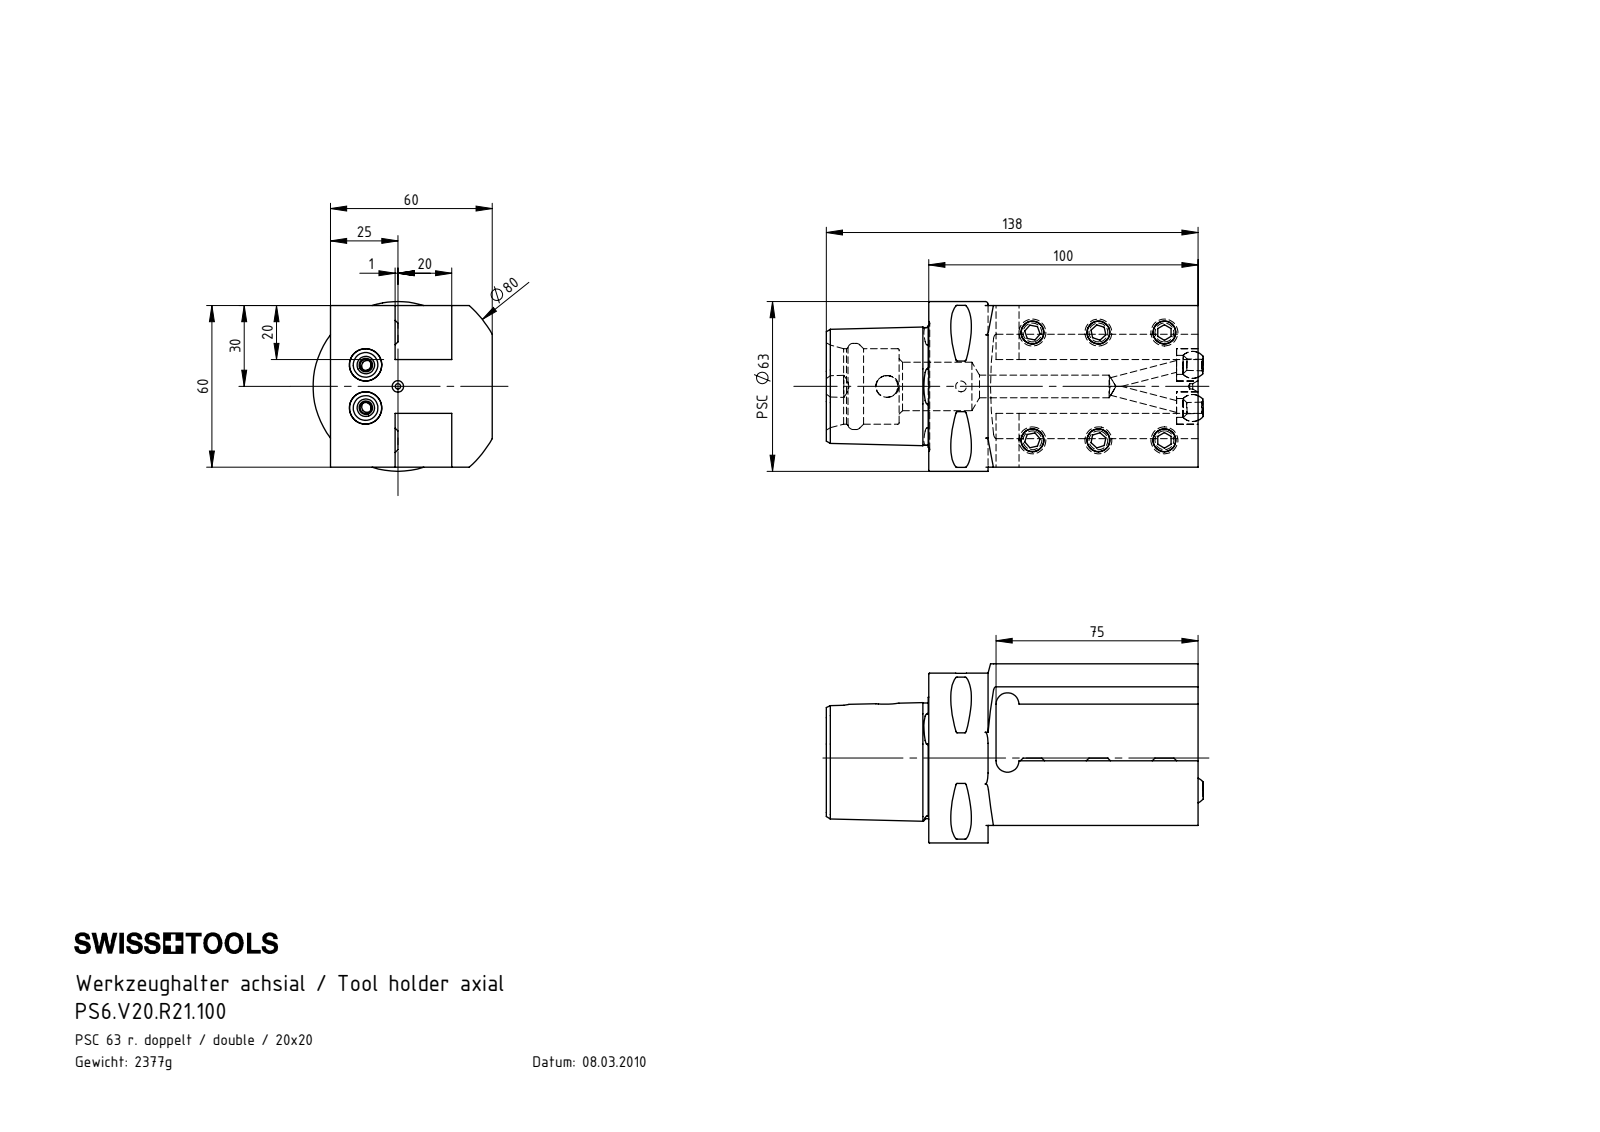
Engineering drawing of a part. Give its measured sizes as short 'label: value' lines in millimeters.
name: KU1-U12.001.010_2; KU1-U12.001.010; ISO 4026 - M10 x 25; KU1-U12.001.010_1 (+2 more)
written by: SolidWorks 2017 (AUTOMOTIVE_DESIGN)
unit: mm
bodies: 11 solids, 306 faces (96 planar, 84 cylindrical, 126 other)
size: 139.8 × 66.5 × 63
volume: 301 991 mm³; area: 59 030 mm²
holes: 6× ⌀8.5, 4× ⌀4.2, 2× ⌀7, 2× ⌀12, 1× ⌀2, 1× ⌀4, 1× ⌀8.1, 1× ⌀8.4, 1× ⌀18, 1× ⌀28, 1× ⌀32
bosses: 6× ⌀10, 1× ⌀63
rounds: 8× R0.5, 3× R0.8, 2× R5.2, 1× R6, 1× R40
face distances: 60, 20, 40, 15, 45, 36, 21, 24, 100, 25
hole spacings: 24.5, 46.91, 40, 14.42, 33.2, 49, 54.78, 57.58
